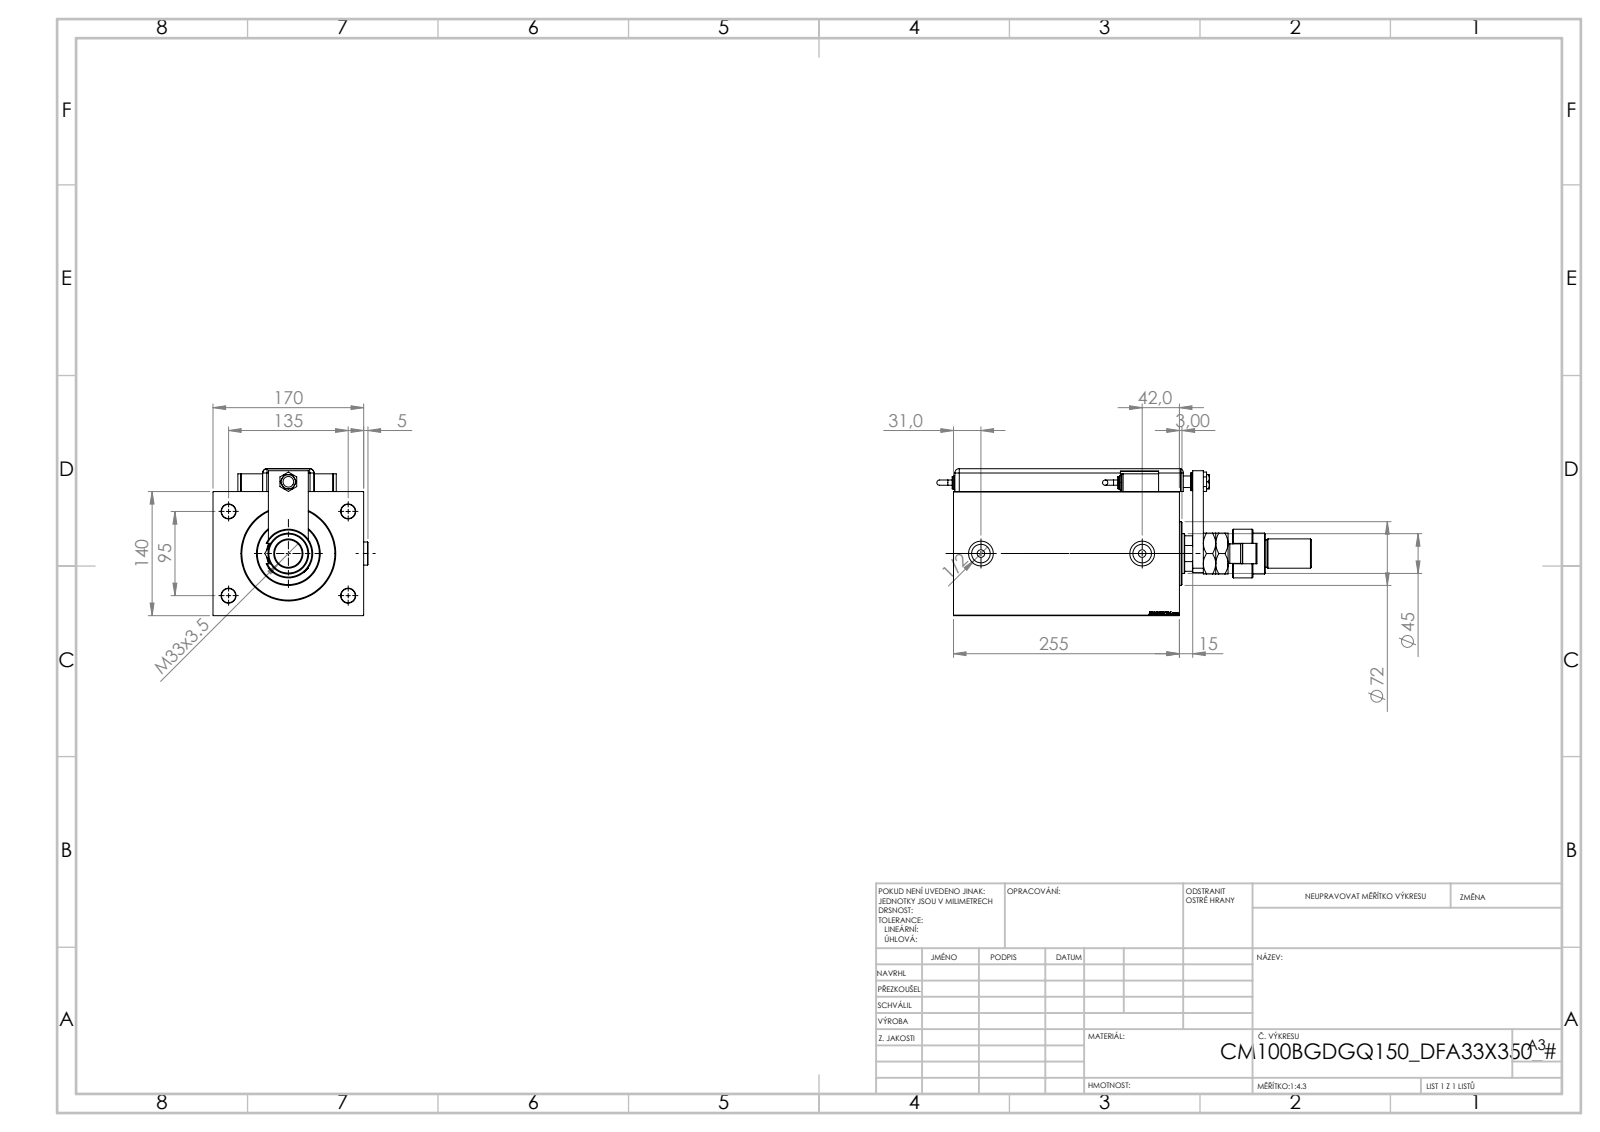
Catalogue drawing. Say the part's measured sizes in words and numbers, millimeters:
The part is named "Zatka_OIL_PORT; NUT_D19; V450CM_B_Body; MFA (+7 more)". Its 3-D file was written by "SolidWorks 2019 (CONFIG_CONTROL_DESIGN)". It is 17 solids with 1407 faces: 670 planar, 140 cylindrical and 597 other. Overall it measures 422.76 by 174.9 by 165.8 millimeters. Its volume is 5 469 000 cubic millimeters and its surface area 516 696 square millimeters. Round holes: 4 of diameter 16, 2 of diameter 4, 2 of diameter 8, 2 of diameter 8.5, 2 of diameter 20.96, 2 of diameter 28, 1 of diameter 12, 1 of diameter 13, 1 of diameter 14, 1 of diameter 31.5, 1 of diameter 33, 1 of diameter 39. Round bosses or shafts: 3 of diameter 20, 2 of diameter 26, 2 of diameter 16, 2 of diameter 14, 2 of diameter 6, 1 of diameter 72, 1 of diameter 55, 1 of diameter 46. Partial cylindrical surfaces (rounded edges, fillets, slot ends): 9 of radius 5, 1 of radius 10, 1 of radius 11.5, 1 of radius 22. The main face-to-face distances are 140, 170, 3, 255, 26, 229, 15, 165.8, 25.8, 56. The hole center spacings are 82.54, 75.36, 95, 135, 145.15, 165.08, 20, 81.
